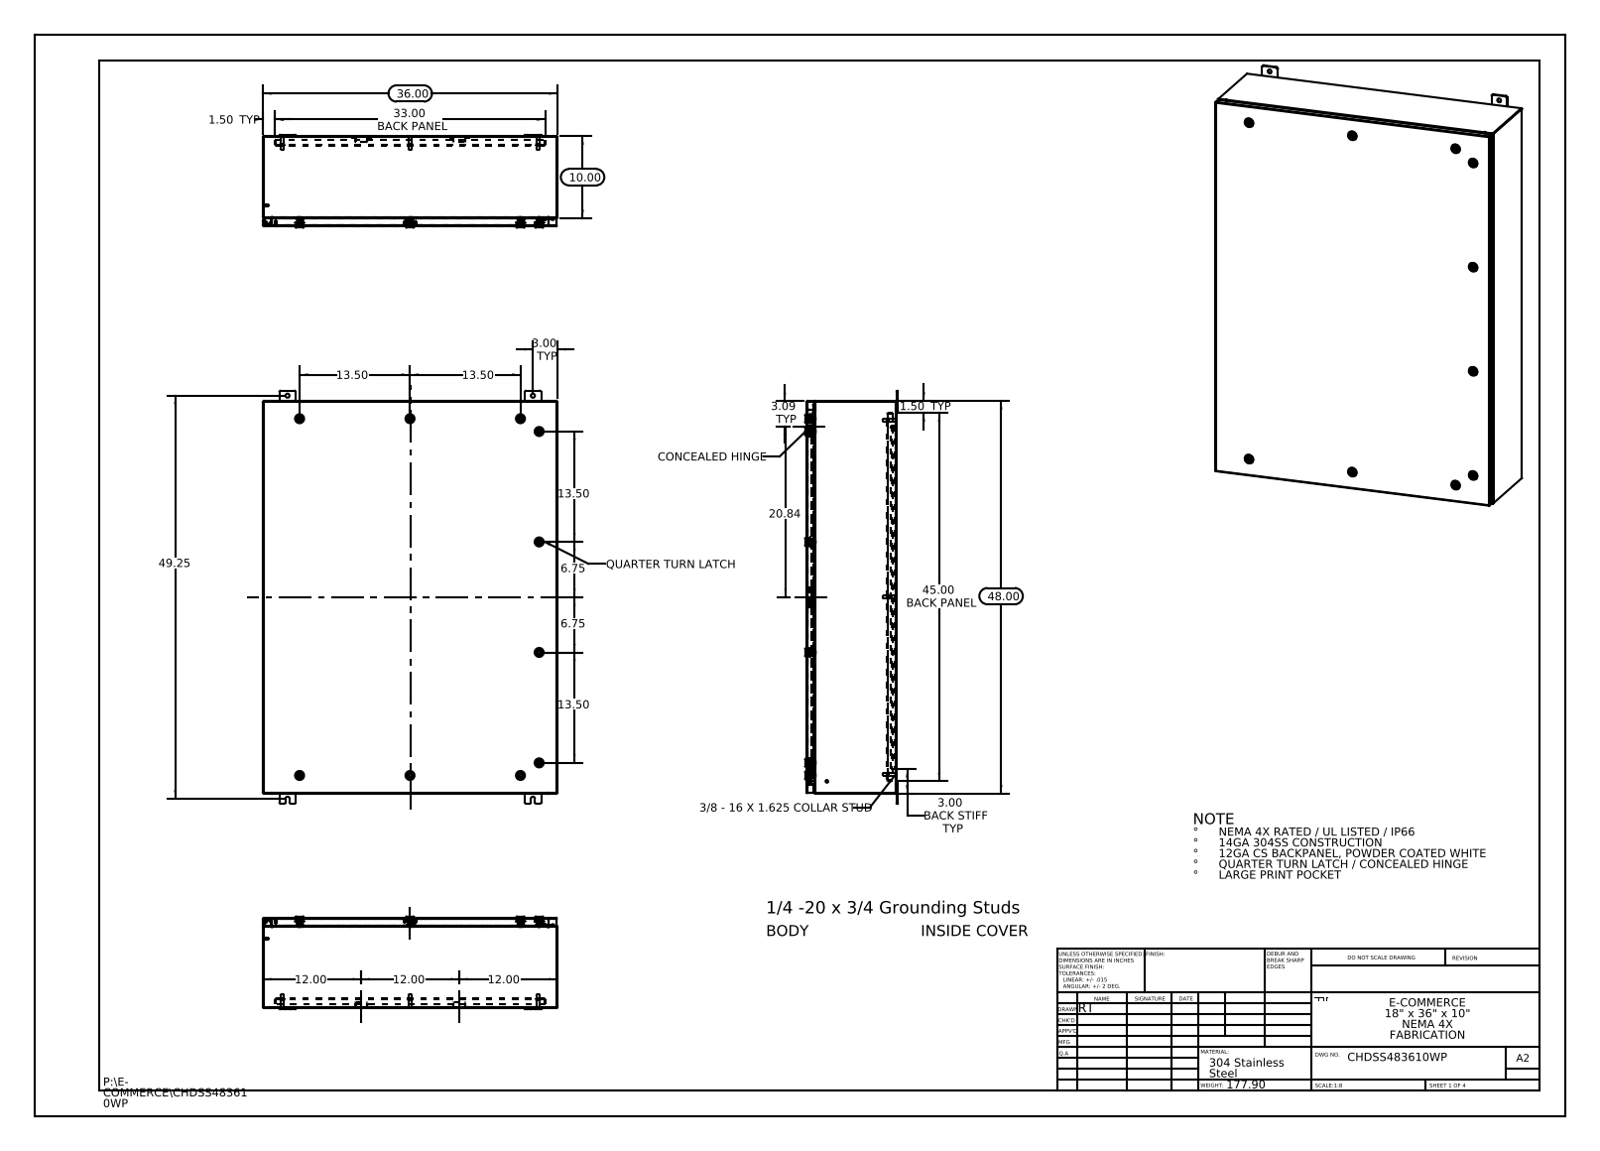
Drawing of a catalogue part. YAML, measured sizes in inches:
part_name: "Concealed Hinge (Cover Side); 10_30 CD Stud; Washer-221320-IB-Industrilas_Washer-221320-IB-Industrilas; CHDSS483610WP Mounting Studs (+8 more)"
step_written_by: "SolidWorks 2013 (CONFIG_CONTROL_DESIGN)"
units: inches
bodies: {solids: 94, faces: 9060, planar: 2626, cylindrical: 2826, other: 3608}
overall_size: [50.5, 36, 11.356]
volume: 628.3
surface_area: 15572
round_holes:
  - {diameter: 0.5, count: 12}
  - {diameter: 0.197, count: 10}
  - {diameter: 0.394, count: 10}
  - {diameter: 0.4, count: 10}
  - {diameter: 0.63, count: 10}
  - {diameter: 0.787, count: 10}
  - {diameter: 0.136, count: 6}
  - {diameter: 0.25, count: 6}
  - {diameter: 0.211, count: 1}
round_bosses_or_shafts:
  - {diameter: 0.236, count: 12}
  - {diameter: 1.102, count: 10}
  - {diameter: 0.78, count: 10}
  - {diameter: 0.626, count: 10}
  - {diameter: 0.61, count: 10}
  - {diameter: 0.531, count: 10}
  - {diameter: 0.392, count: 10}
  - {diameter: 0.114, count: 10}
partial_cylinders:
  - {radius: 0.006, count: 330}
  - {radius: 0.118, count: 330}
  - {radius: 0.028, count: 120}
  - {radius: 0.02, count: 40}
  - {radius: 0.197, count: 40}
  - {radius: 0.013, count: 34}
  - {radius: 0.088, count: 30}
  - {radius: 0.19, count: 24}
face_to_face_distances: [0.075, 0.074, 10.861, 10.936, 11.01, 10.935, 0.104, 1, 1.075, 9.861]
hole_center_spacings: [13.5, 20, 20.123, 21.625, 27, 38.003, 45.642, 45.986]
